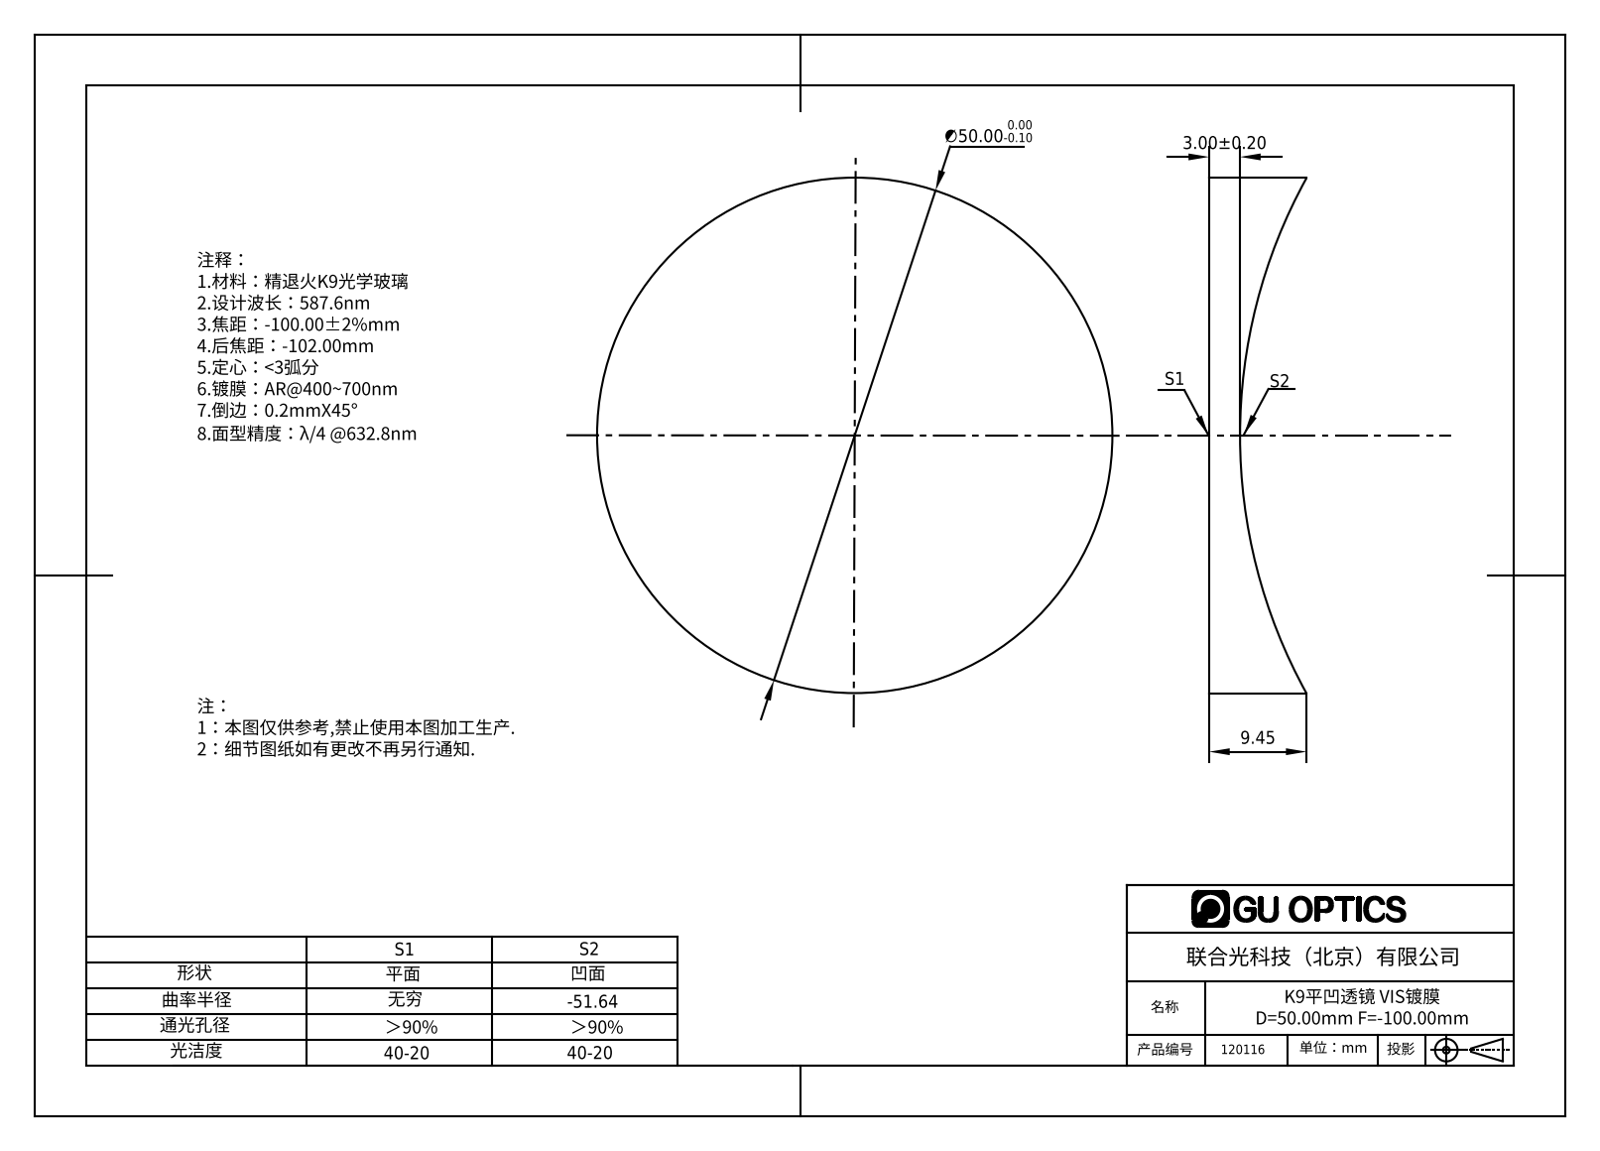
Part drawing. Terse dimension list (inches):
name: 120056
written by: SolidWorks 2016 (AUTOMOTIVE_DESIGN)
unit: in
bodies: 1 solid, 5 faces (1 planar, 2 cylindrical, 2 other)
size: 1.969 × 1.969 × 0.372
volume: 0.738 in³; area: 8.592 in²
bosses: 1× ⌀1.969
